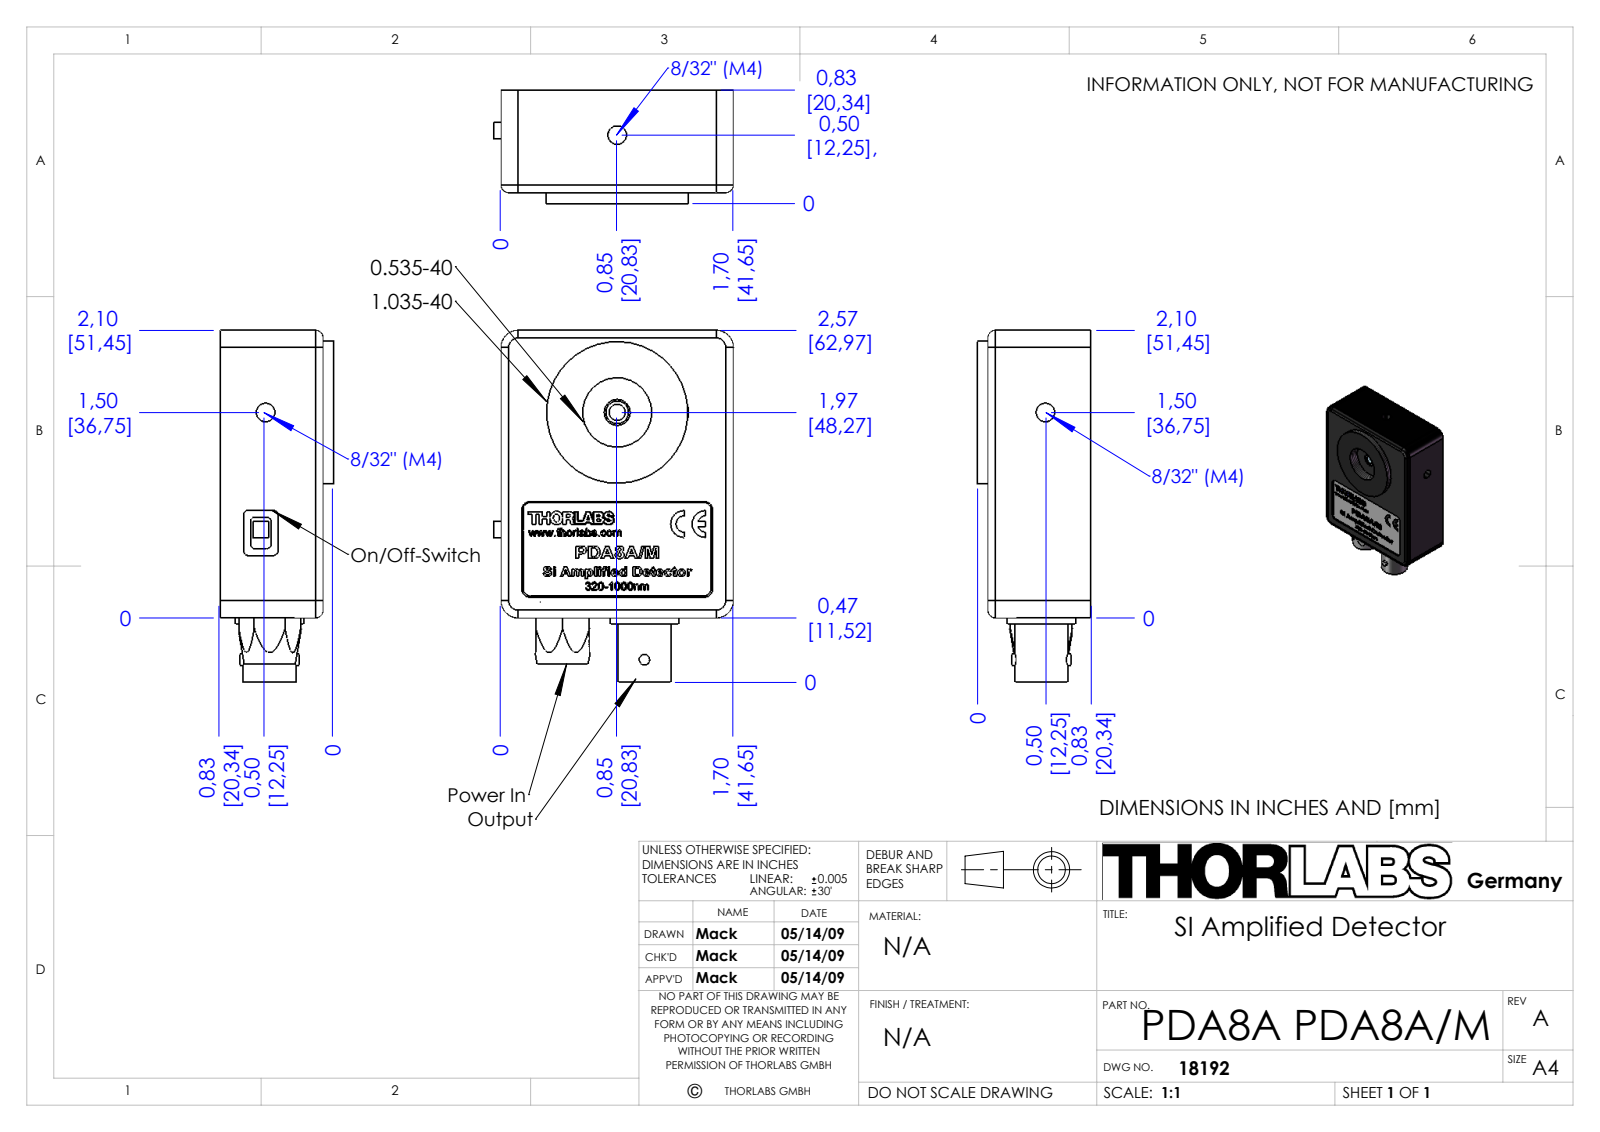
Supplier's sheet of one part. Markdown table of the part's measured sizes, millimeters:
| quantity | value |
| --- | --- |
| part name | BaugruppePDA8A-M |
| STEP written by | SolidWorks 2016 (AUTOMOTIVE_DESIGN) |
| units | millimeters |
| bodies | 13 solids, 1508 faces (802 planar, 246 cylindrical, 460 other) |
| overall size | 65.3 × 44.64 × 21.08 |
| volume | 20 076 mm³ |
| surface area | 20 800 mm² |
| round holes (diameter × count) | 1.6 × 7, 1 × 5, 2.4 × 4, 3.45 × 2, 1.27 × 1, 1.32 × 1, 3 × 1, 3.15 × 1, 4.2 × 1, 4.85 × 1, 6 × 1, 8 × 1 |
| round bosses / shafts (diameter × count) | 3 × 6, 0.51 × 6, 0.45 × 2, 26.29 × 1, 12.45 × 1, 10.92 × 1, 9.6 × 1, 9.4 × 1 |
| partial cylindrical surfaces (radius × count) | 3.17 × 32, 3.3 × 12, 0.79 × 8, 2.41 × 8, 1.27 × 4, 1.4 × 4, 0.61 × 3, 1.59 × 3 |
| main face-to-face distances | 1.59, 2.54, 1.27, 17.27, 15.68, 18.54, 16.95, 1.78, 0.51, 19.05 |
| hole center spacings | 1.75, 1.27, 2.47, 5.14, 18.28, 19.32, 20.01, 20.04 |
